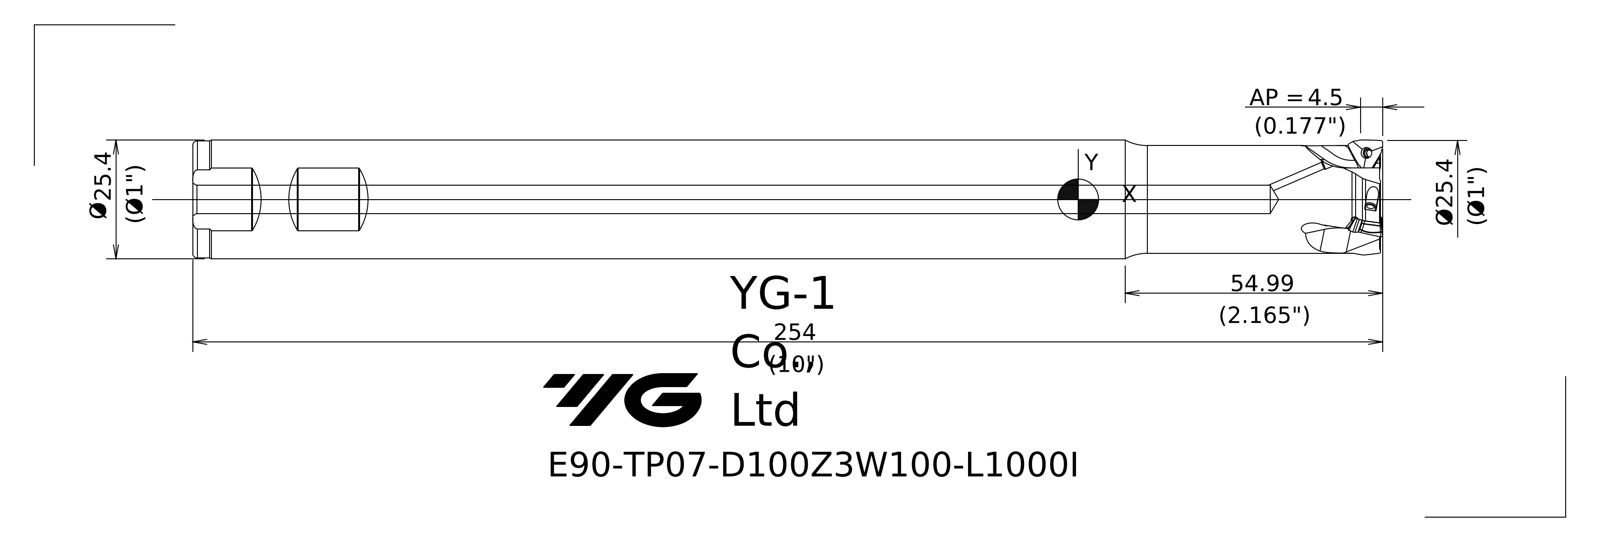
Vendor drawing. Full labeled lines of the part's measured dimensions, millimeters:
Part name (STEP PRODUCT): 102268DC2902ywo7
STEP written by: SIEMENS PLM Software NX 10.0 (AP203_CONFIGURATION_CONTROLLED_3D_DESIGN_OF_MECHANICAL_PARTS_AND_ASSEMBLIES_MIM_LF)
Units: millimetres
Bodies: 1 solid, 51 faces (8 planar, 8 cylindrical, 35 other)
Overall size (bounding box): 254 × 25.45 × 25.45
Volume: 116 645 mm³ · Surface area: 26 523 mm²
Round holes (diameter × count): ⌀1.5 ×1, ⌀6 ×1
Round bosses / shafts (diameter × count): ⌀25.4 ×1, ⌀25 ×1, ⌀23 ×1
Partial cylindrical surfaces — rounded edges, fillets, slot ends (radius × count): R0.3 ×3
Main face-to-face distances: 253.35, 253.5, 16.14
